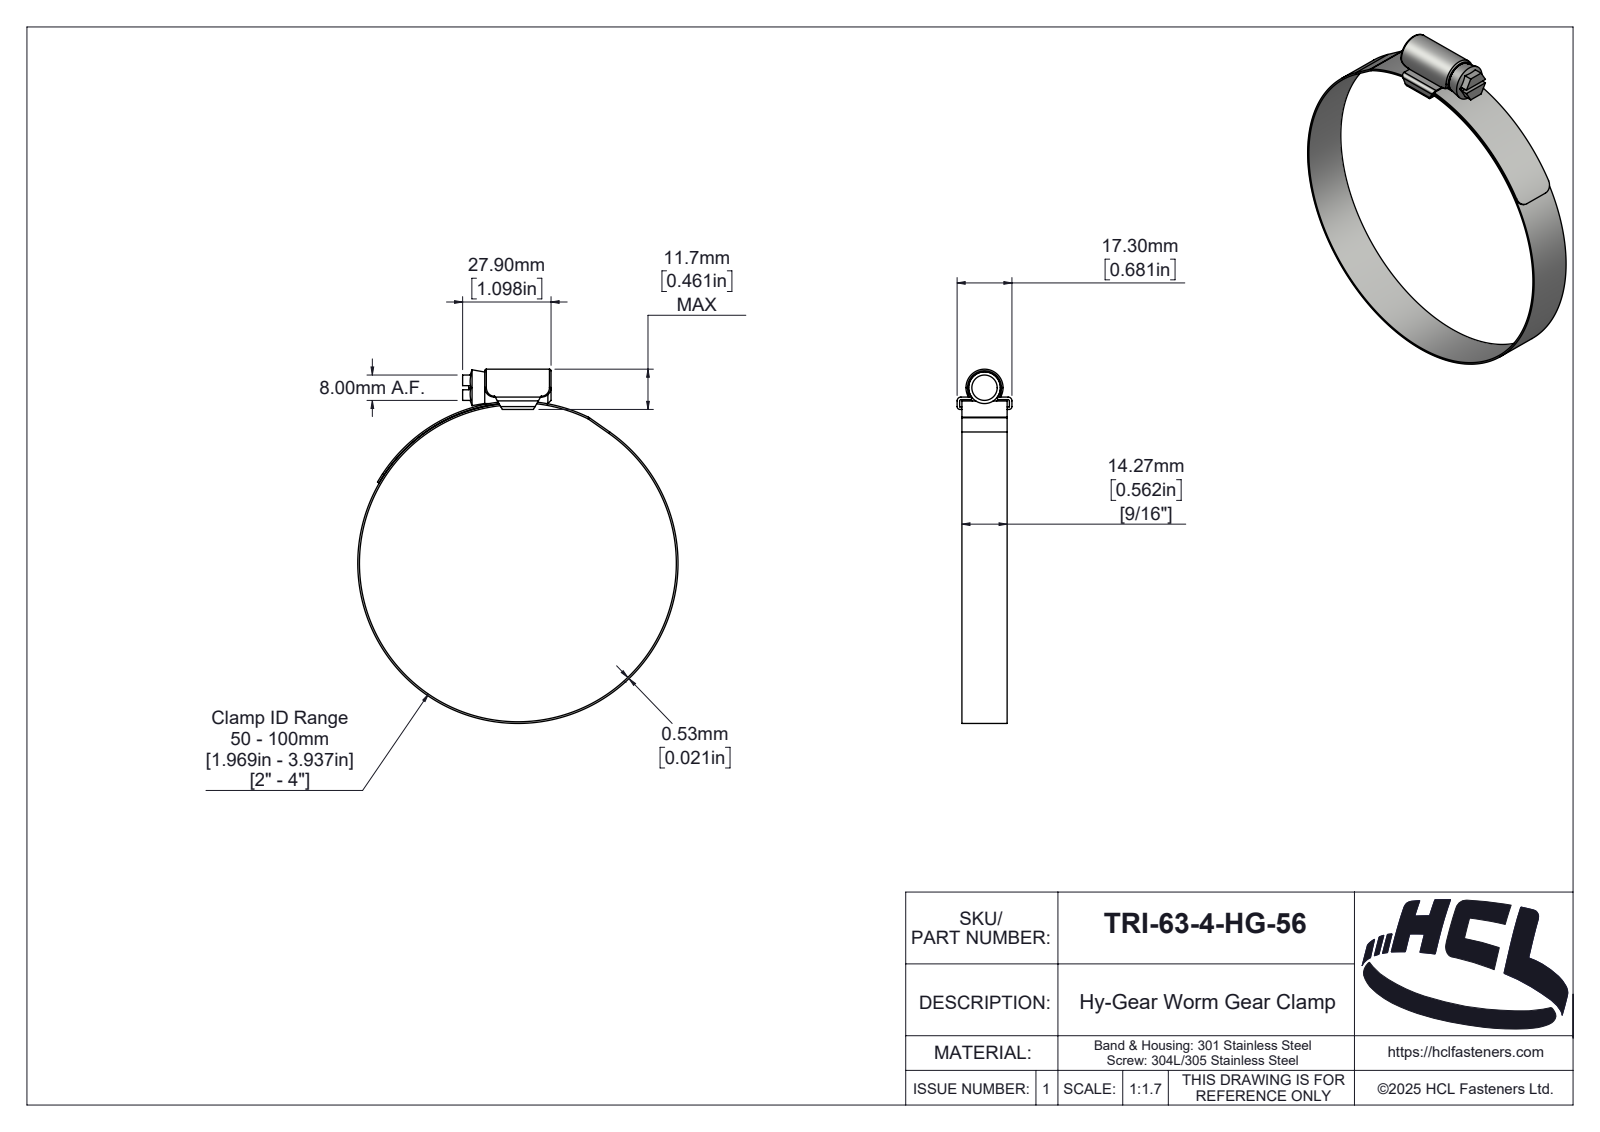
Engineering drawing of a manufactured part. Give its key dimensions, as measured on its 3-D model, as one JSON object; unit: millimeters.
{"part_name": "TRI-50-0-HG-56", "step_written_by": "SolidWorks 2025 (AUTOMOTIVE_DESIGN)", "units": "millimeters", "bodies": {"solids": 3, "faces": 189, "planar": 39, "cylindrical": 89, "other": 61}, "overall_size": [111.73, 101.06, 17.3], "volume_mm3": 5584, "surface_area_mm2": 13735, "round_holes": [[100, 1]], "round_bosses_or_shafts": [[101.06, 1], [10, 1]], "partial_cylinders_radius": [[0.5, 6], [3, 4], [0.1, 2], [0.9, 2], [1.2, 2], [0.46, 1], [1.89, 1], [2, 1]], "face_to_face_distances": [0.8, 14.26, 3.1, 0.53, 2.3, 3.9, 27.9, 1.52, 15.78, 16.5]}
